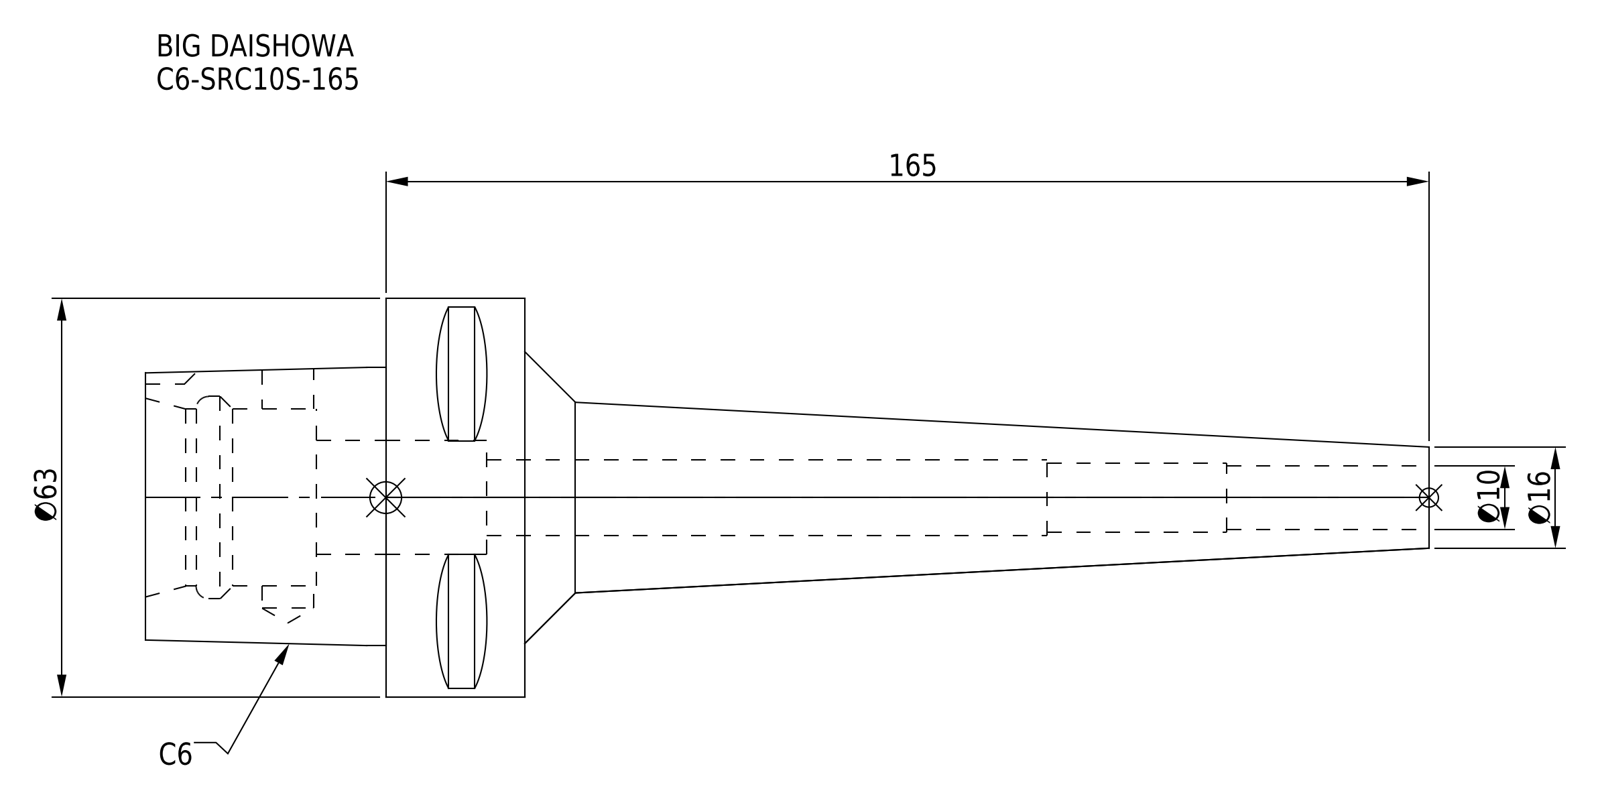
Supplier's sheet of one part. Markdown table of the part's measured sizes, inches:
| quantity | value |
| --- | --- |
| part name | C6-SRC10S-165 |
| STEP written by | CREO PARAMETRIC BY PTC INC, 2016380 (AUTOMOTIVE_DESIGN) |
| units | inches |
| bodies | 1 solid, 65 faces (30 planar, 21 cylindrical, 14 other) |
| overall size | 7.992 × 2.48 × 2.48 |
| volume | 9.084 in³ |
| surface area | 54.25 in² |
| round holes (diameter × count) | 0.319 × 1, 0.394 × 1, 0.433 × 1, 0.472 × 1, 0.709 × 1, 1.102 × 1, 1.26 × 1 |
| round bosses / shafts (diameter × count) | 2.48 × 1 |
| partial cylindrical surfaces (radius × count) | 0.197 × 1 |
| main face-to-face distances | 0.866, 1.063, 2.362, 1.496, 1.299, 0.433, 0.98, 2.181, 0.236, 0.63 |
